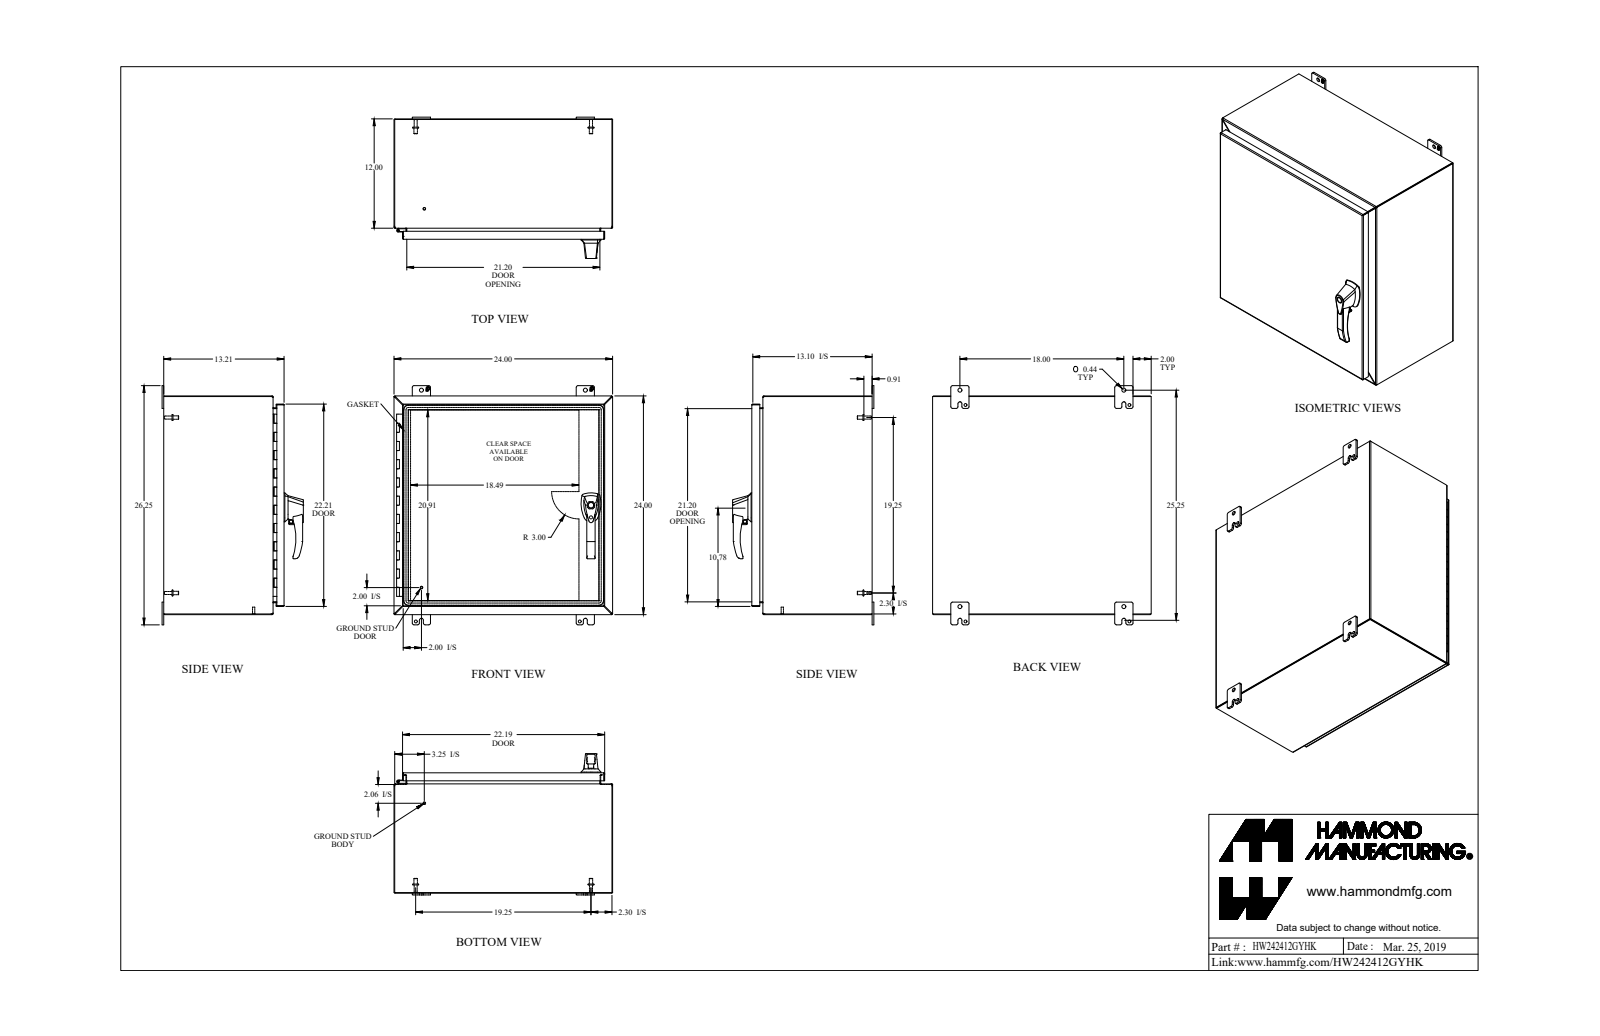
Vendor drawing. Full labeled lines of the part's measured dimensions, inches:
Part name (STEP PRODUCT): HW242412GYHK
STEP written by: SolidWorks 2018 (AUTOMOTIVE_DESIGN)
Units: inches
Bodies: 43 solids, 1400 faces (675 planar, 559 cylindrical, 166 other)
Overall size (bounding box): 26.25 × 24 × 15.512
Volume: 216.4 in³ · Surface area: 5 576 in²
Round holes (diameter × count): ⌀0.176 ×6, ⌀0.25 ×4, ⌀0.313 ×4, ⌀0.196 ×3, ⌀0.265 ×3, ⌀0.413 ×3, ⌀0.256 ×2, ⌀0.394 ×2, ⌀0.437 ×2, ⌀0.187 ×1, ⌀0.233 ×1, ⌀0.334 ×1
Round bosses / shafts (diameter × count): ⌀0.375 ×9, ⌀0.25 ×6, ⌀0.156 ×6, ⌀0.65 ×4, ⌀0.33 ×4, ⌀1 ×3, ⌀0.63 ×2, ⌀0.51 ×2
Partial cylindrical surfaces — rounded edges, fillets, slot ends (radius × count): R0.25 ×31, R0.188 ×24, R0.036 ×18, R0.108 ×18, R0.06 ×12, R0.125 ×9, R0.04 ×8, R0.218 ×8
Main face-to-face distances: 0.072, 23.928, 23.856, 24, 0.072, 13.138, 13.066, 13.21, 13.138, 11.928
Hole centre spacings: 8.118, 8.119, 16.237, 1.111, 8.119, 9.236, 18, 1.005
